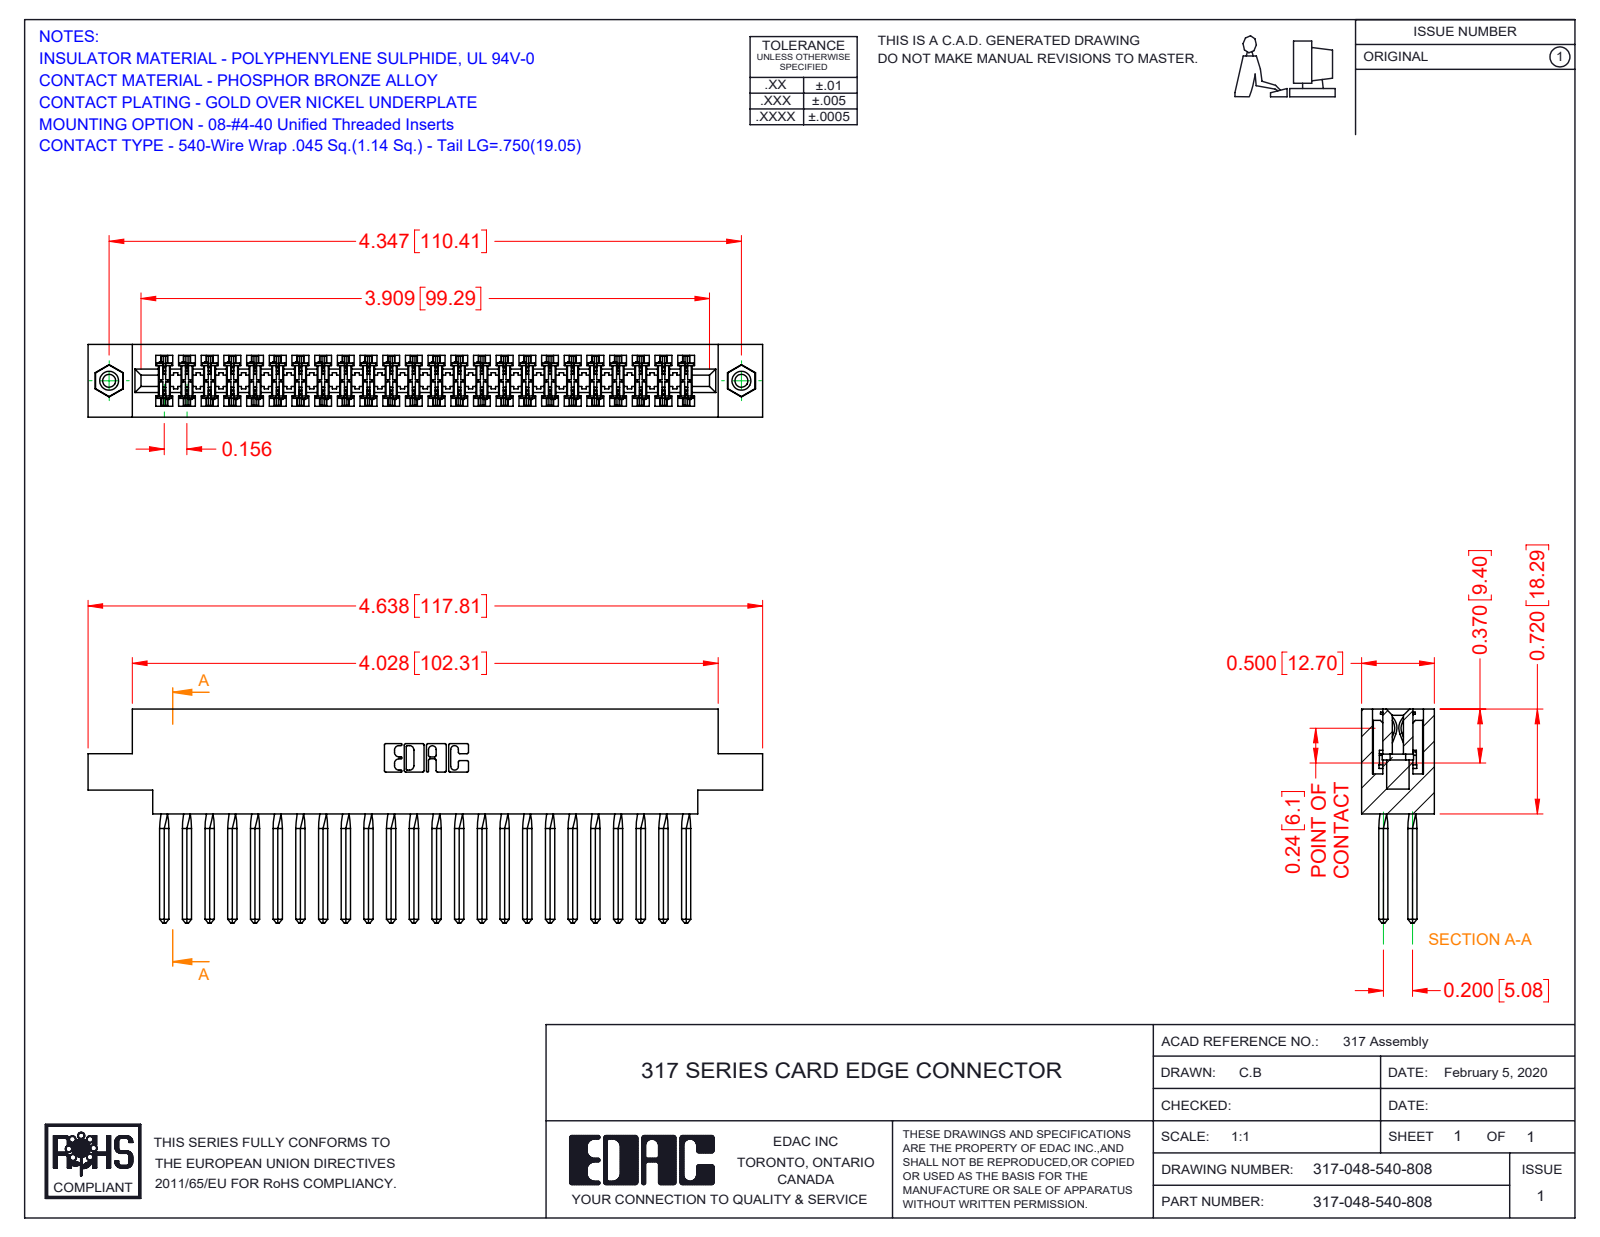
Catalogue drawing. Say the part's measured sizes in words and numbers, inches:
The part is named "317-290-001_540; 345-250-001_345-250-003-102; 317-048-540-808; 317 Part_.156 Dia - TI". Its 3-D file was written by "SolidWorks 2016 (CONFIG_CONTROL_DESIGN)". It is 51 solids with 4434 faces: 3594 planar, 632 cylindrical and 208 other. Overall it measures 4.638 by 1.47 by 0.5 inches. Its volume is 1.169 cubic inches and its surface area 43.25 square inches. Round holes: 2 of diameter 0.089, 2 of diameter 0.125, 2 of diameter 0.156. Round bosses or shafts: 2 of diameter 0.155. Partial cylindrical surfaces (rounded edges, fillets, slot ends): 96 of radius 0.015, 22 of radius 0.01, 6 of radius 0.007, 6 of radius 0.031, 3 of radius 0.026, 2 of radius 0.095, 2 of radius 0.1, 2 of radius 0.11. The main face-to-face distances are 0.5, 0.075, 0.425, 0.35, 0.11, 0.195, 0.094, 0.72, 0.2, 0.115. The hole center spacings are 4.347.
